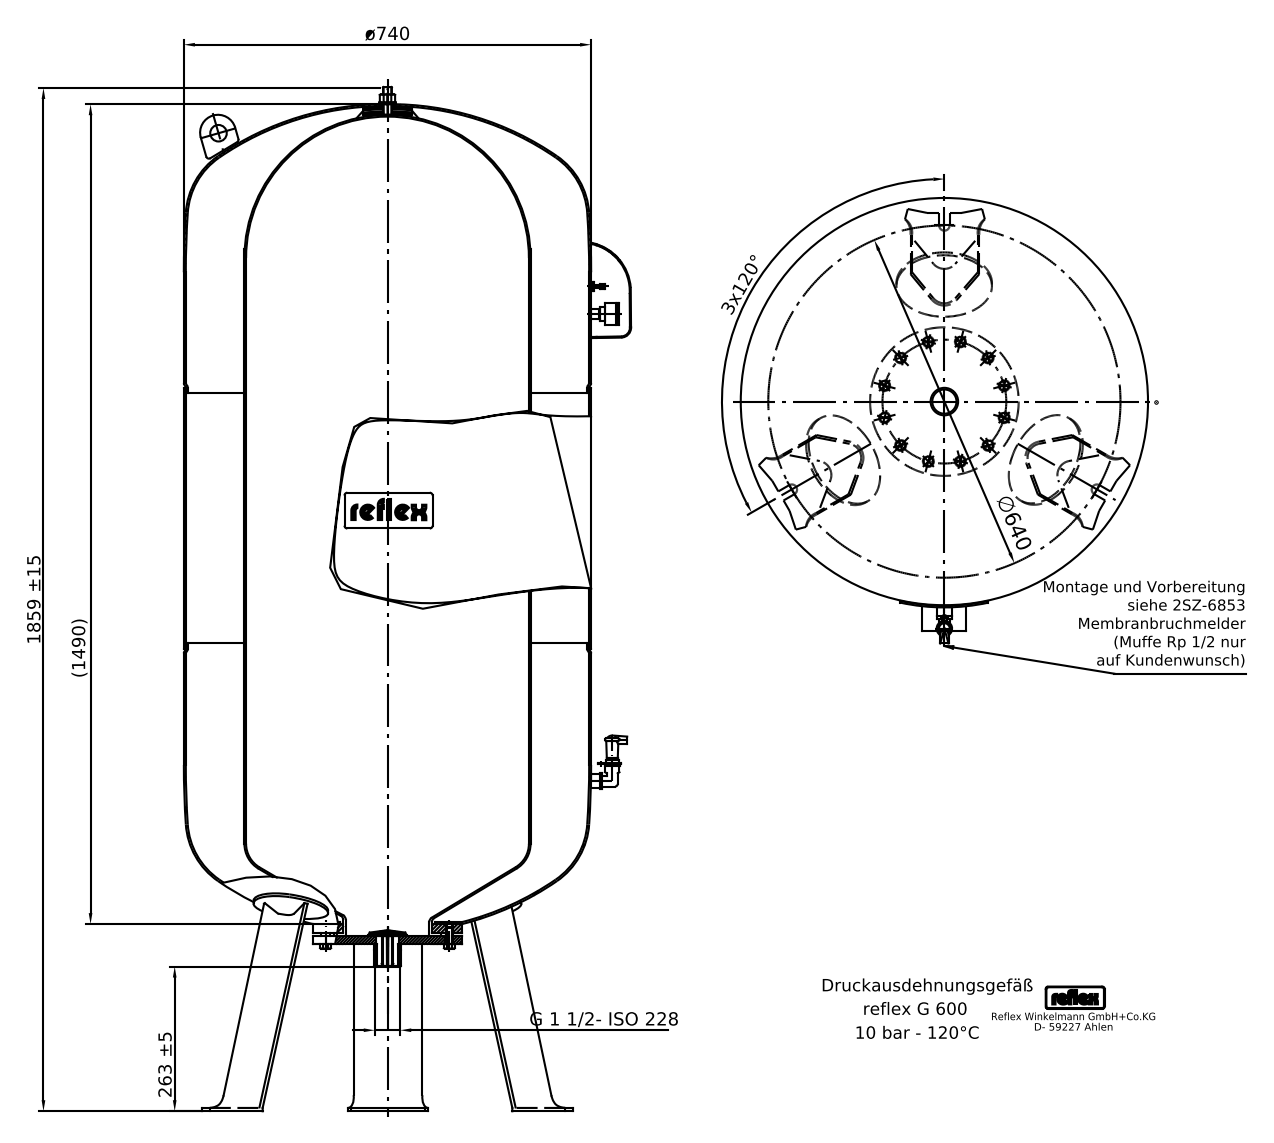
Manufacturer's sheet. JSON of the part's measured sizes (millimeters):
{"step_written_by": "Mechanical Desktop 2008 (CONFIG_CONTROL_DESIGN)", "units": "millimeters", "bodies": {"solids": 22, "faces": 480, "planar": 242, "cylindrical": 150, "other": 88}, "overall_size": [1859, 812, 741.14], "volume_mm3": 595500000, "surface_area_mm2": 6522000, "round_holes": [[10, 1], [160, 1]], "round_bosses_or_shafts": [[16, 13], [20, 3], [28, 2], [26, 2], [24, 2], [740, 1], [270, 1], [48.3, 1]], "partial_cylinders_radius": [[25, 18], [3.94, 4], [1.57, 3], [9, 3], [2.69, 2], [4.72, 2], [6.49, 2], [6.58, 2]], "face_to_face_distances": [1127, 16, 21, 195, 1322, 5.97, 5.89, 211, 1338, 5], "hole_center_spacings": [385.5]}
